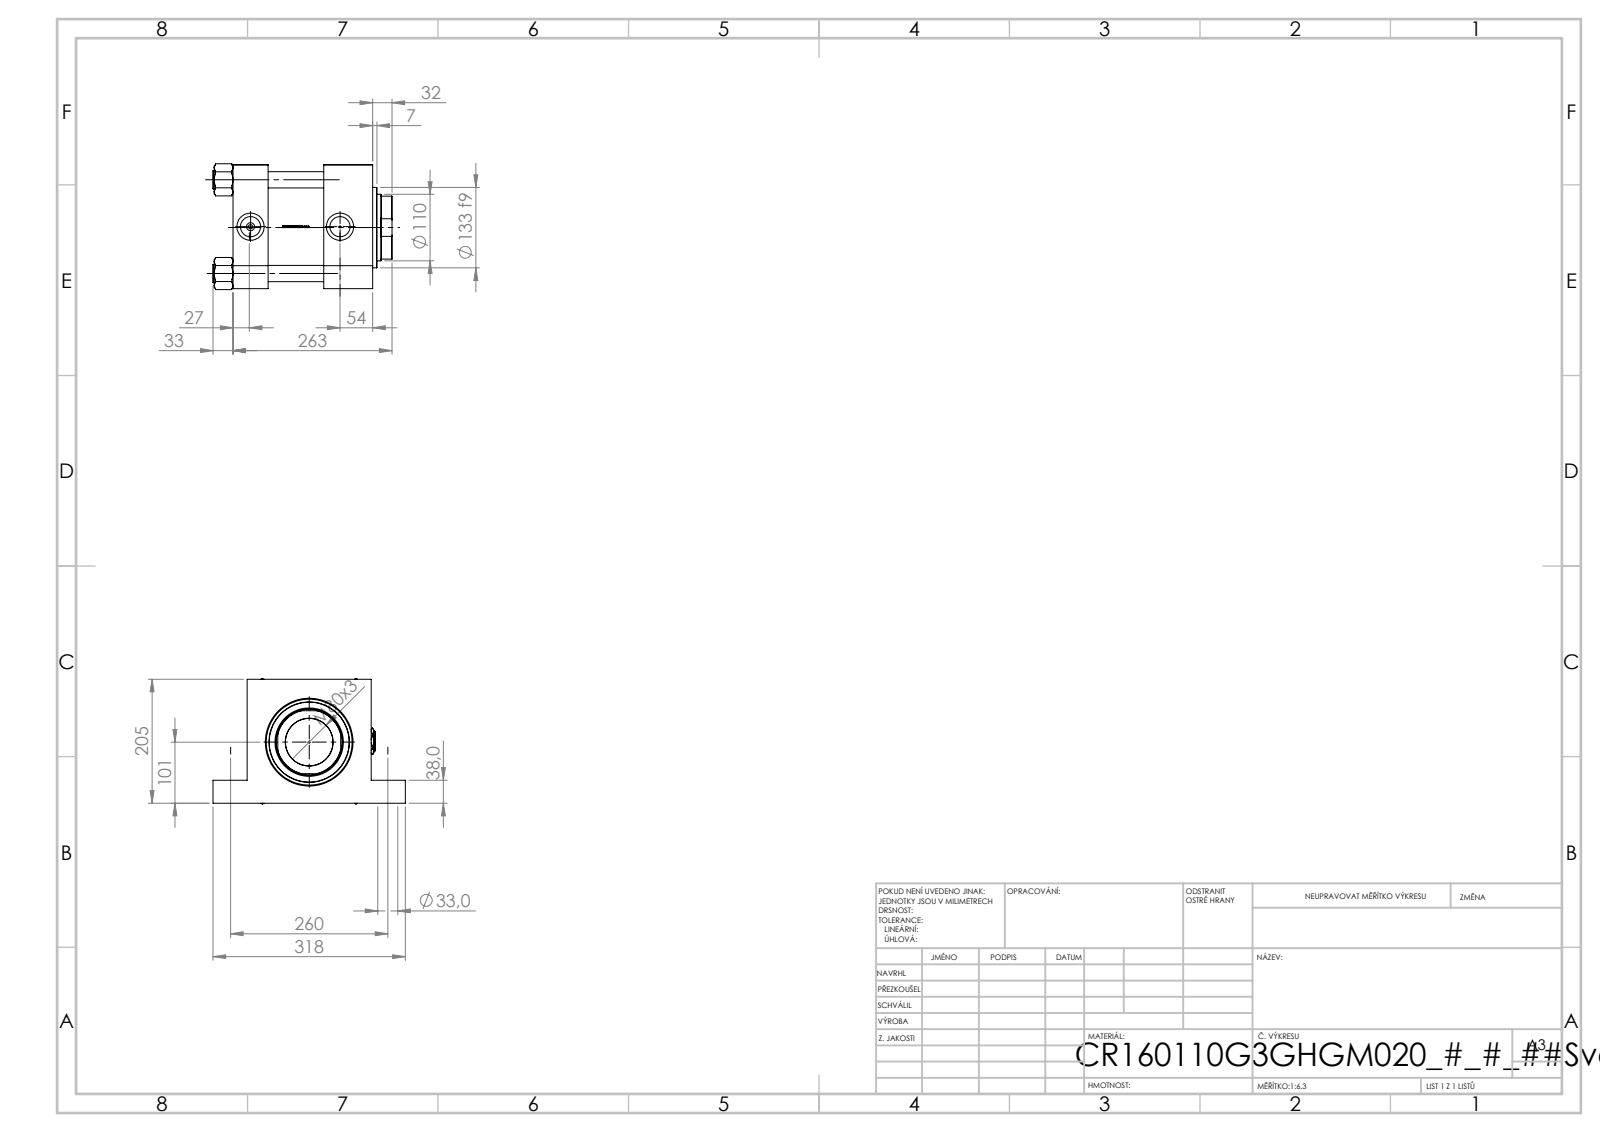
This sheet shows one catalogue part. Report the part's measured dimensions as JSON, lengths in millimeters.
{"part_name": "V215CR_G_TYCINKA; V215CR_G_Body; Zatka_pro_OIL_PORT; V215CR_VCP_G (+2 more)", "step_written_by": "SolidWorks 2019 (CONFIG_CONTROL_DESIGN)", "units": "millimeters", "bodies": {"solids": 13, "faces": 1231, "planar": 525, "cylindrical": 132, "other": 574}, "overall_size": [318, 296, 208.14], "volume_mm3": 8150000, "surface_area_mm2": 780086, "round_holes": [[27, 4], [33, 4], [7, 2], [33.24, 2], [45, 2], [78.5, 1], [110, 1], [113, 1], [120, 1], [142, 1], [160, 1]], "round_bosses_or_shafts": [[30, 4], [166, 1], [133, 1]], "partial_cylinders_radius": [[54, 1]], "face_to_face_distances": [205, 58, 231, 173, 81, 150, 92, 38, 167, 202.3], "hole_center_spacings": [154.9, 108.48, 110.6, 150, 219.06, 260, 300.17, 148]}
